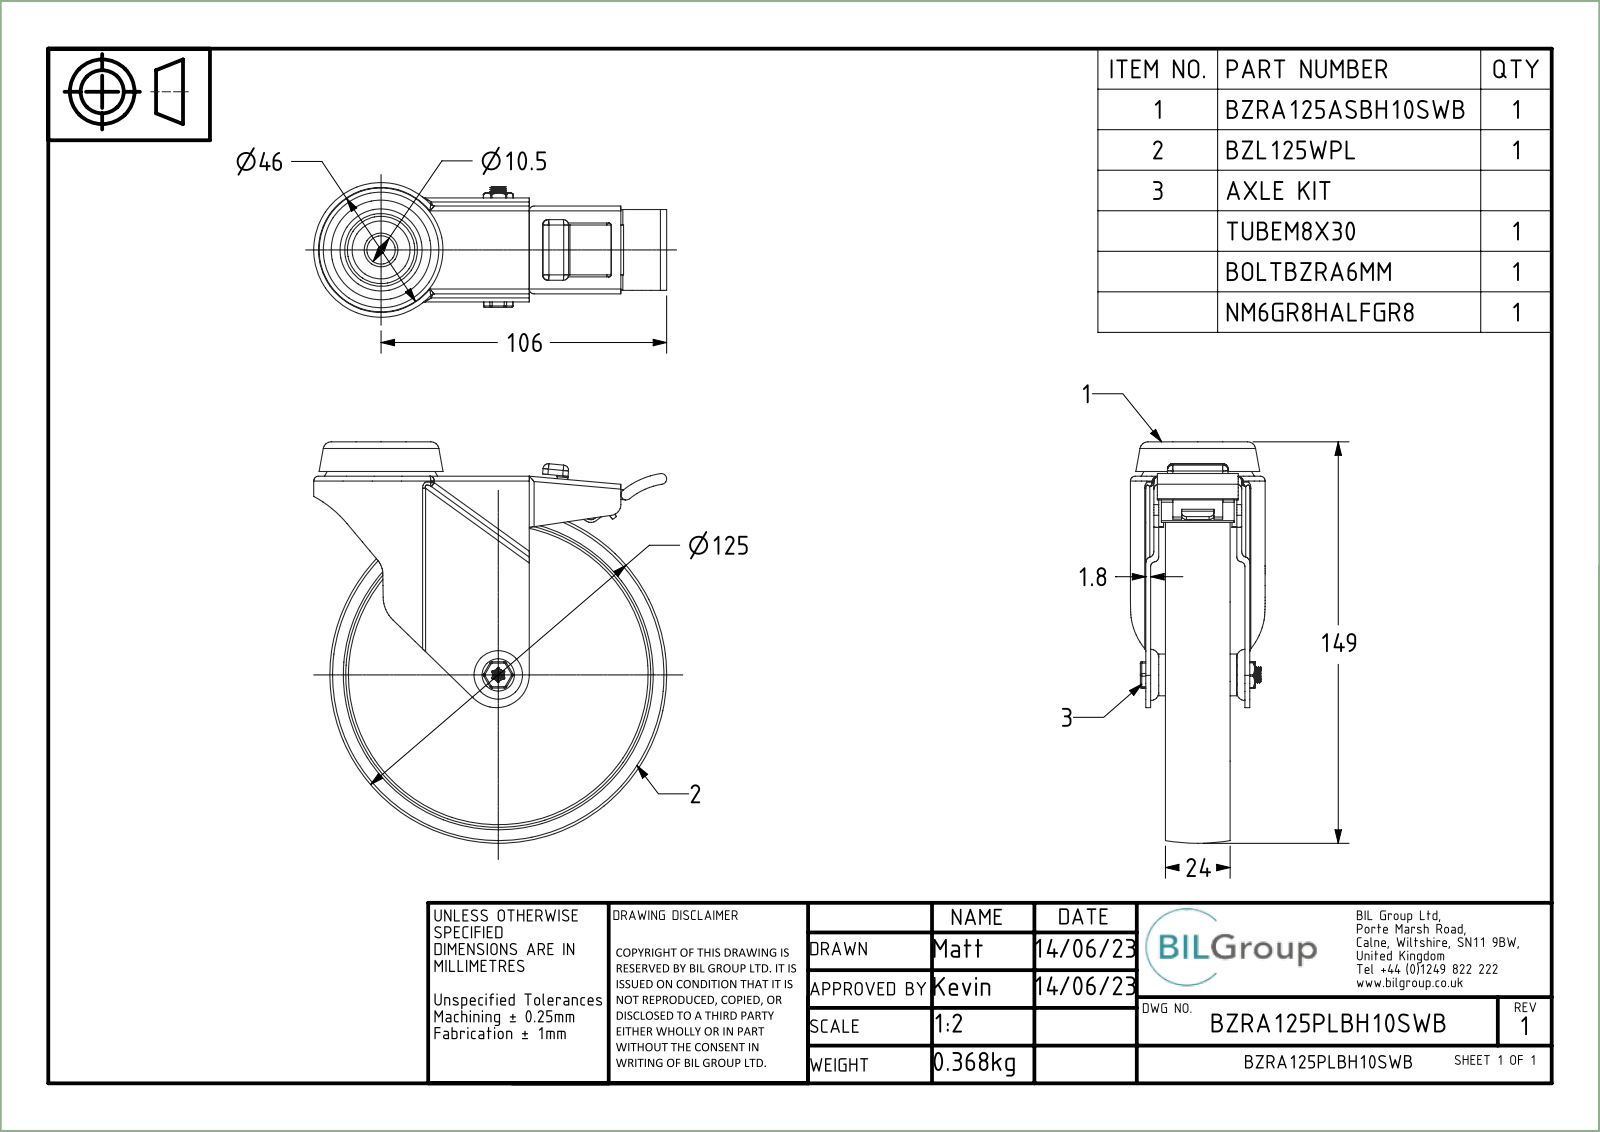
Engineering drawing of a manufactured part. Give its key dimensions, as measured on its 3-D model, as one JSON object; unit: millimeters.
{"part_name": "BZRA125ASBH10SWB; ZINC PLATED PRESSED STEEL HEAD; ZINC PLATED PRESSED STEEL FORKS; ZINC PLATED PRESSED STEEL BRAKE (+8 more)", "step_written_by": "Spatial InterOp 3D (CONFIG_CONTROL_DESIGN)", "units": "millimeters", "bodies": {"solids": 9, "faces": 623, "planar": 214, "cylindrical": 250, "other": 159}, "overall_size": [149, 131, 50], "volume_mm3": 157146, "surface_area_mm2": 88763, "round_holes": [[6, 1], [6.3, 1], [6.4, 1], [8.2, 1], [8.3, 1], [10.5, 1], [10.56, 1], [28, 1], [39, 1]], "round_bosses_or_shafts": [[18, 1], [15.5, 1], [14.76, 1], [8, 1], [7.95, 1], [5, 1]], "partial_cylinders_radius": [[1, 23], [1.8, 23], [0.5, 14], [0.9, 11], [2, 11], [0.4, 6], [2.12, 1], [2.28, 1]], "face_to_face_distances": [6, 1.8, 33.8, 3, 16.3, 22.3, 4.8, 11.5, 17.5, 32]}
